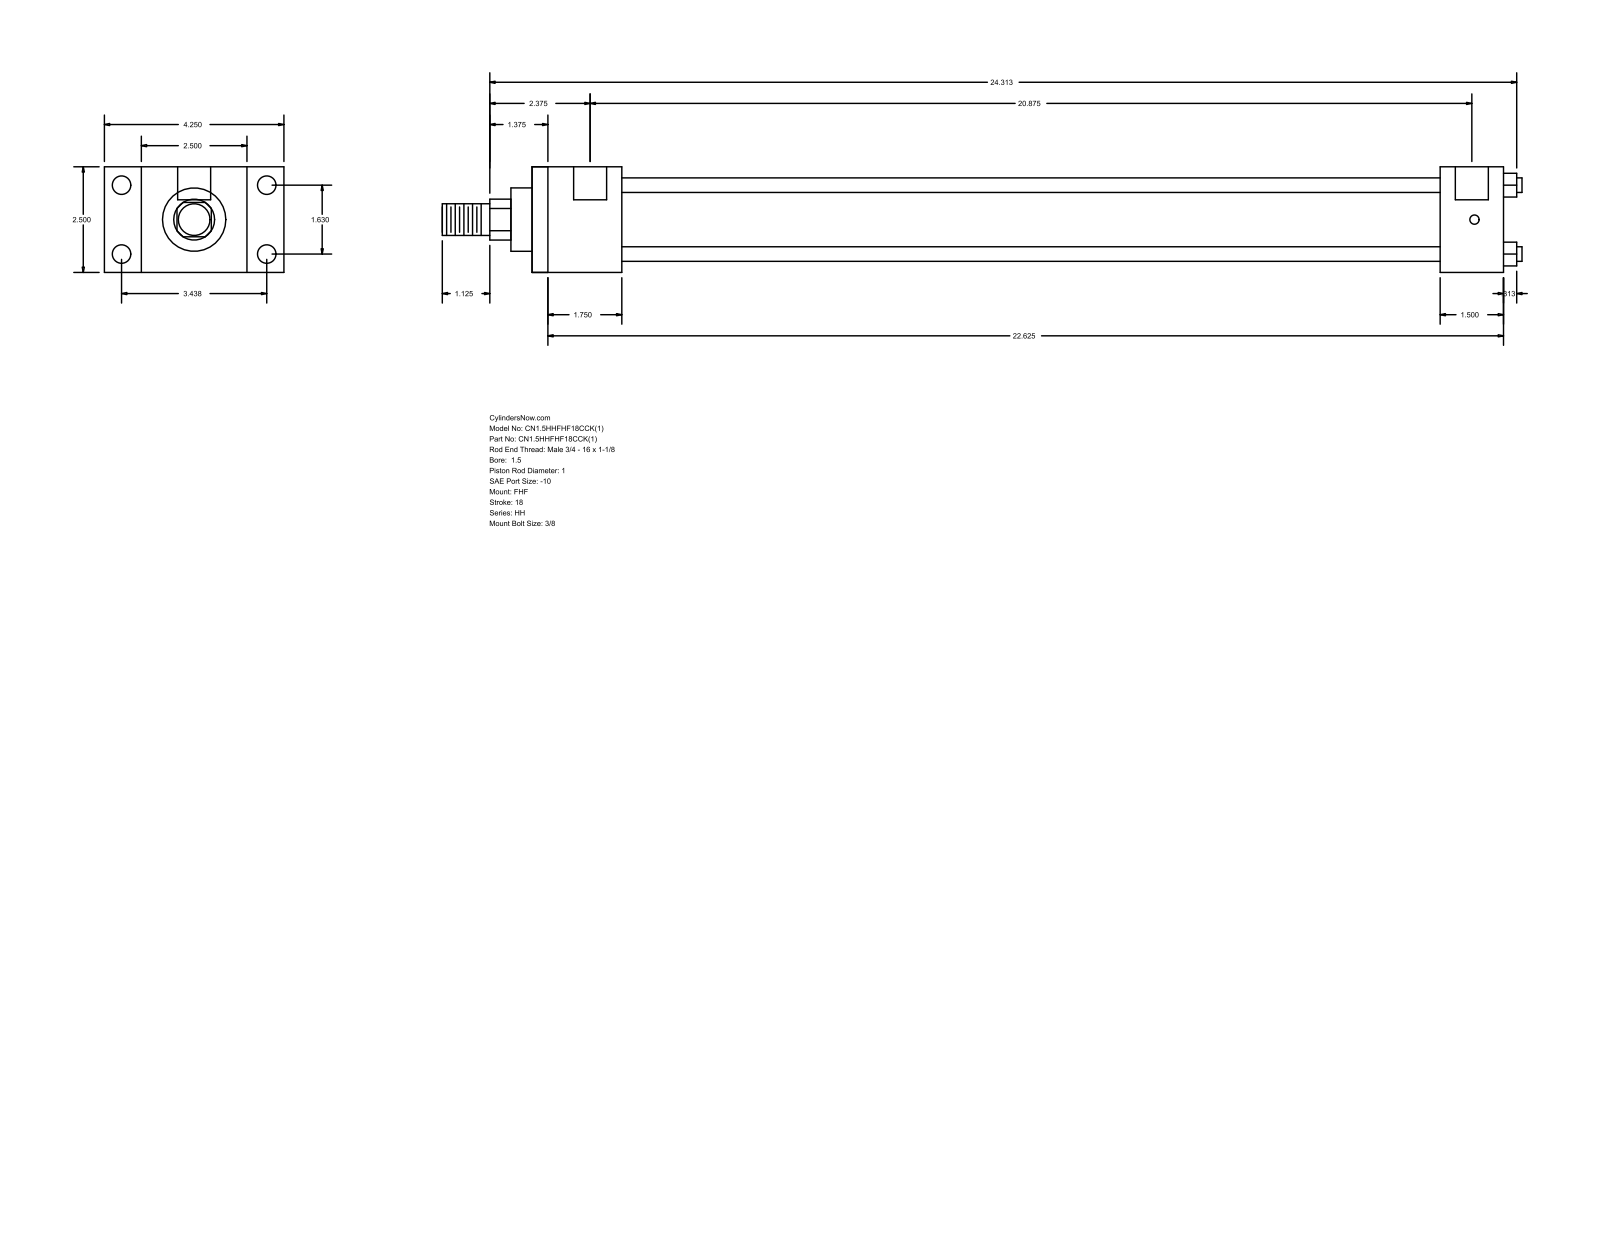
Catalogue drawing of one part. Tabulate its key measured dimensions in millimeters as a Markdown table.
| quantity | value |
| --- | --- |
| part name | HH_FHF__0150_1 |
| STEP written by | GSSL Pune (CONFIG_CONTROL_DESIGN) |
| units | millimeters |
| bodies | 0 solids, 88 faces (60 planar, 28 cylindrical, 0 other) |
| overall size | 649.29 × 107.95 × 63.5 |
| round holes (diameter × count) | 5.56 × 4, 11.13 × 4, 19.84 × 2 |
| round bosses / shafts (diameter × count) | 8.76 × 4, 44.45 × 1, 38.1 × 1, 25.4 × 1, 19.05 × 1 |
| partial cylindrical surfaces (radius × count) | 12.29 × 1 |
| main face-to-face distances | 63.5, 22.23, 85.73, 53.98, 107.96, 584.2, 530.22, 38.1, 546.1, 492.12 |
| hole center spacings | 1.59, 41.4, 87.32, 96.64, 531.81, 533.4, 530.22 |
